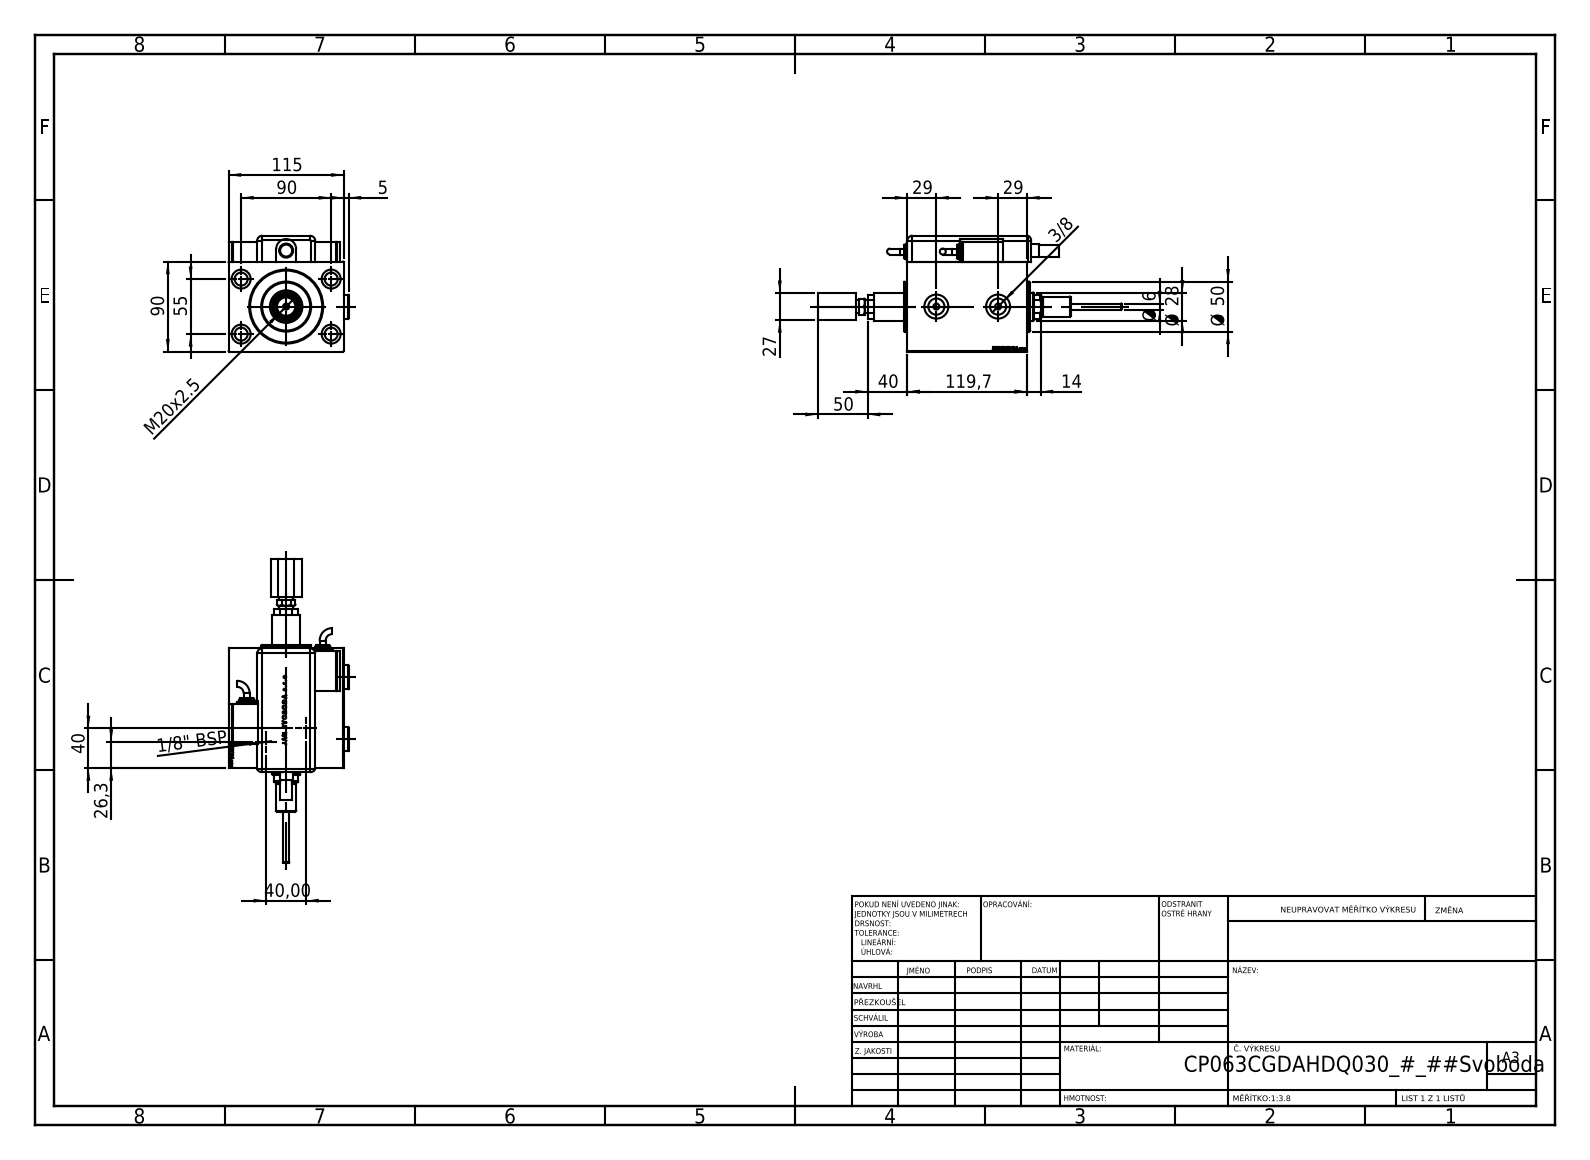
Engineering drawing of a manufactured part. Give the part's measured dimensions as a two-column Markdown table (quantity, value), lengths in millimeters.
| quantity | value |
| --- | --- |
| part name | V450CP_MALE_METRIC; SWITCH Q; MAGNETIC SWITCH Q; V450DCP_B_VCP (+7 more) |
| STEP written by | SolidWorks 2019 (CONFIG_CONTROL_DESIGN) |
| units | millimeters |
| bodies | 13 solids, 1360 faces (660 planar, 165 cylindrical, 535 other) |
| overall size | 303.7 × 119.9 × 115.8 |
| volume | 1 277 000 mm³ |
| surface area | 232 466 mm² |
| round holes (diameter × count) | 4 × 4, 13 × 4, 19 × 4, 6 × 3, 8 × 2, 9.73 × 2, 15 × 2, 16.17 × 2, 24 × 2, 3 × 1, 14 × 1, 18.5 × 1 |
| round bosses / shafts (diameter × count) | 20 × 3, 16 × 2, 14 × 2, 6 × 2, 50 × 1, 18 × 1, 13.47 × 1, 13 × 1 |
| partial cylindrical surfaces (radius × count) | 5 × 9, 10 × 1, 13.5 × 1 |
| main face-to-face distances | 90, 3, 115, 119.7, 1, 17.5, 102.2, 30, 25.8, 115.8 |
| hole center spacings | 52.74, 53.27, 55, 90, 94.85, 105.48, 20, 22.18 |
